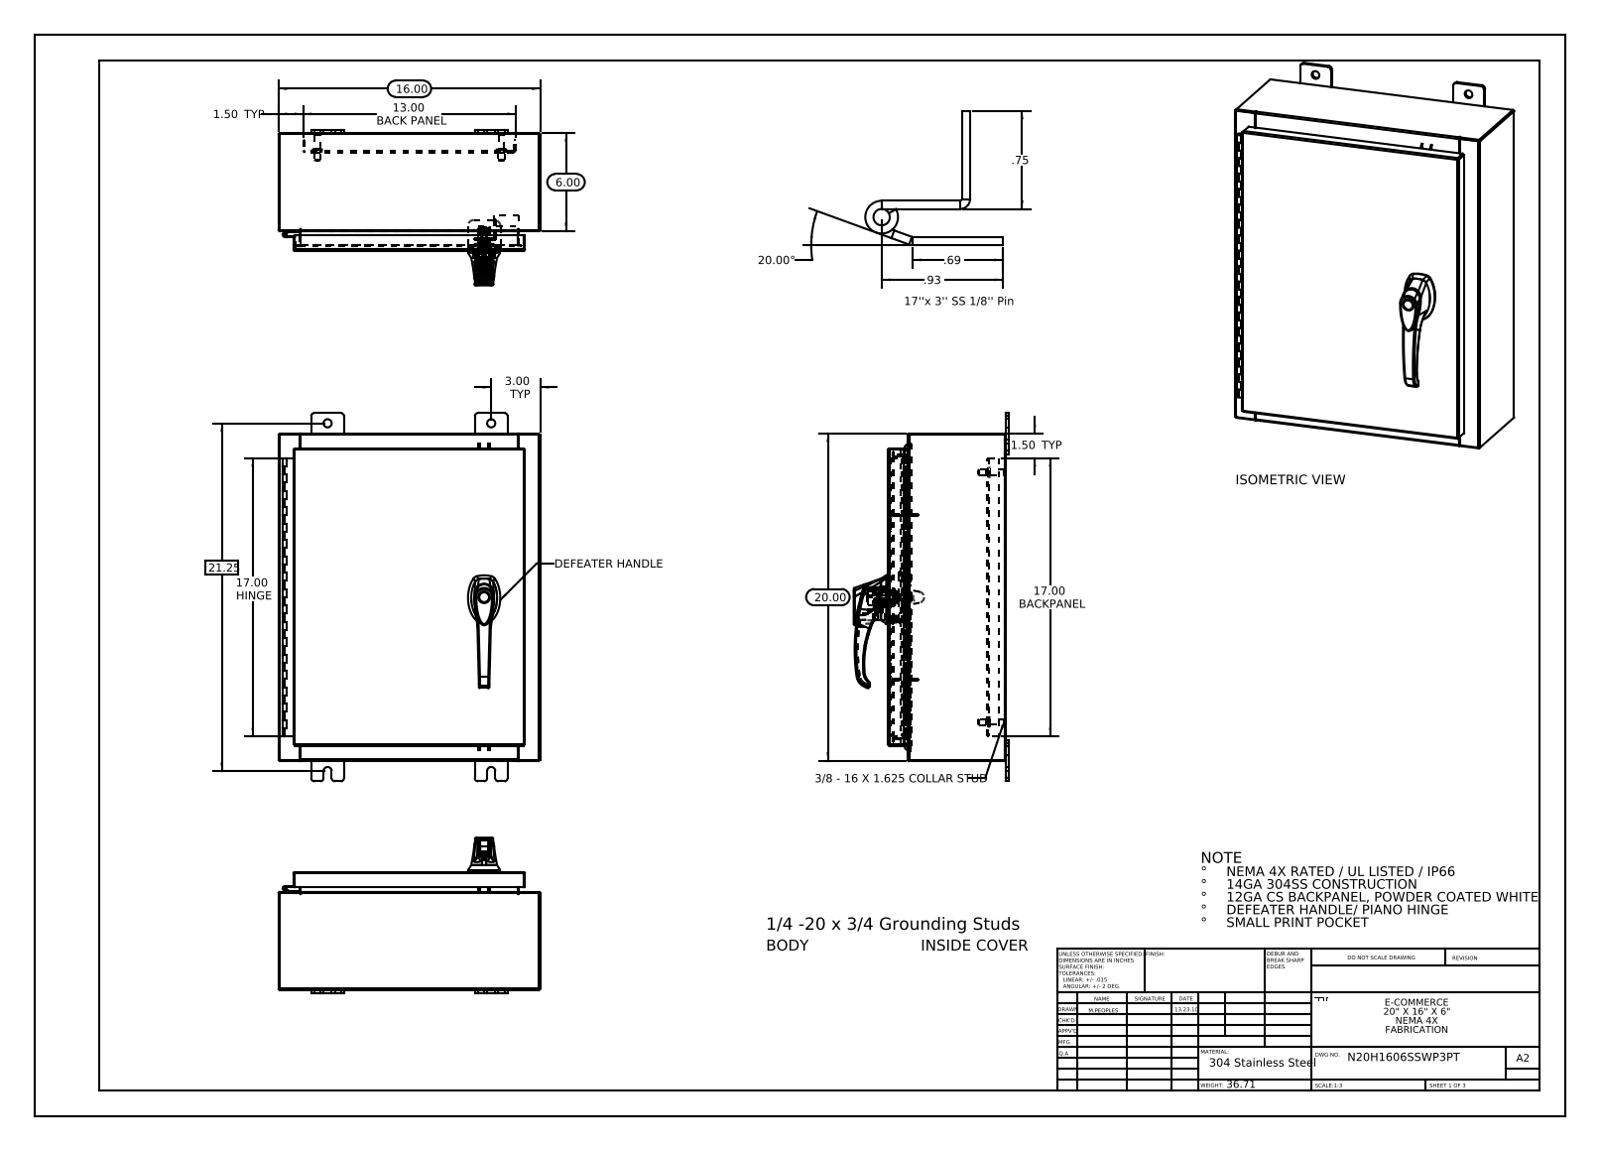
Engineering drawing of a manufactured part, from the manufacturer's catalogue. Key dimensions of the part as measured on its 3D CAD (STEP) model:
Part name (STEP PRODUCT): 297025; N20H1606SSWP3PT Top; 033060_032151; N20H1606SSWP3PT Bottom (+8 more)
STEP written by: SolidWorks 2013 (CONFIG_CONTROL_DESIGN)
Units: inches
Bodies: 31 solids, 2316 faces (817 planar, 845 cylindrical, 654 other)
Overall size (bounding box): 22.5 × 16 × 9.495
Volume: 131.8 in³ · Surface area: 3 230 in²
Round holes (diameter × count): ⌀0.5 ×8, ⌀0.25 ×4, ⌀0.138 ×3, ⌀0.161 ×3, ⌀0.079 ×2, ⌀0.203 ×2, ⌀0.313 ×2, ⌀0.437 ×2, ⌀0.125 ×1, ⌀0.125 ×1, ⌀0.197 ×1, ⌀0.276 ×1
Round bosses / shafts (diameter × count): ⌀0.625 ×4, ⌀0.375 ×4, ⌀0.33 ×4, ⌀1.181 ×1, ⌀0.748 ×1, ⌀0.68 ×1, ⌀0.661 ×1, ⌀0.639 ×1
Partial cylindrical surfaces — rounded edges, fillets, slot ends (radius × count): R0.118 ×37, R0.006 ×33, R0.19 ×24, R0.013 ×22, R0.088 ×18, R0.039 ×15, R0.028 ×12, R0.008 ×6
Main face-to-face distances: 0.075, 7.126, 7.051, 7.201, 0.104, 15.925, 1, 1.075, 6.051, 6.126
Hole centre spacings: 3.404, 11.975, 0.295, 0.625, 0.841, 1.25, 1.313, 1.561
